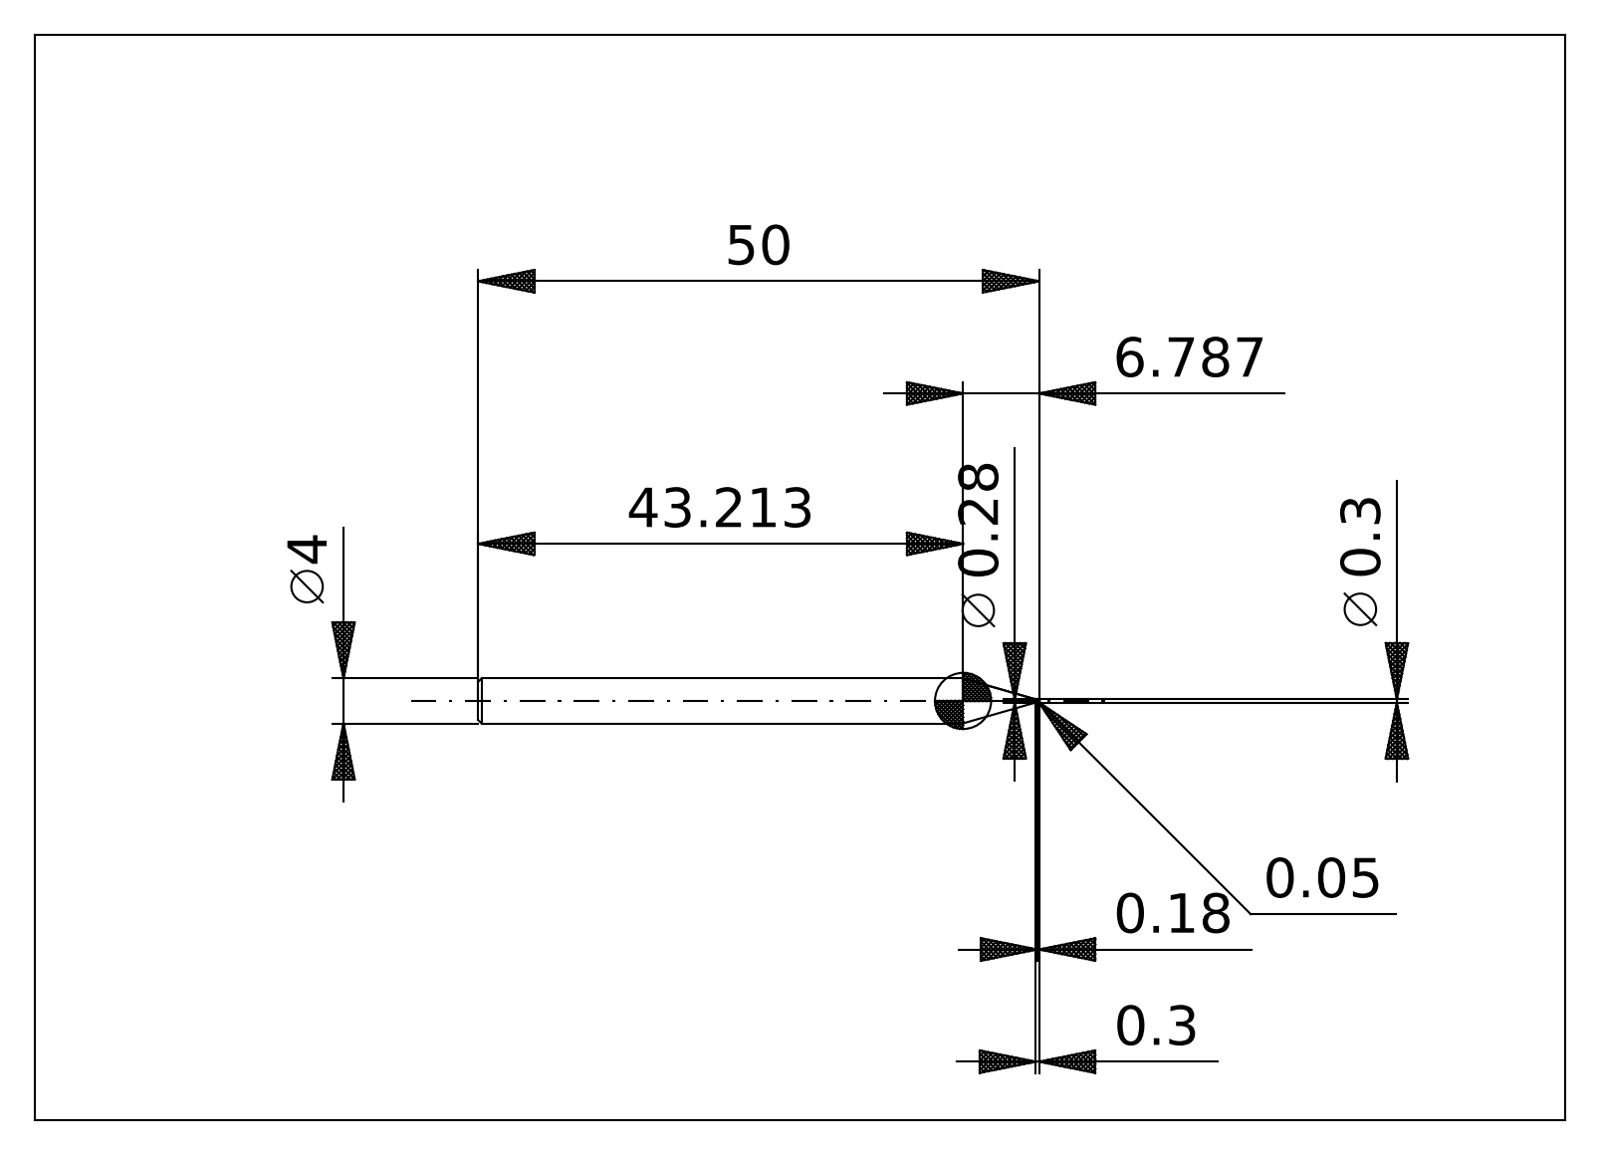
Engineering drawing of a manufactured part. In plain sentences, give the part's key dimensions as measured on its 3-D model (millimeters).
Its 3-D file was written by "ACIS (automotive_design)". It is 2 solids with 26 faces: 6 planar, 8 cylindrical and 12 other. Overall it measures 50 by 4 by 4 millimeters. Its volume is 572 cubic millimeters and its surface area 599 square millimeters. Round bosses or shafts: 1 of diameter 4, 1 of diameter 0.28. The main face-to-face distances are 50, 49.96, 49.82, 6.79, 6.75, 6.61, 43.21.
